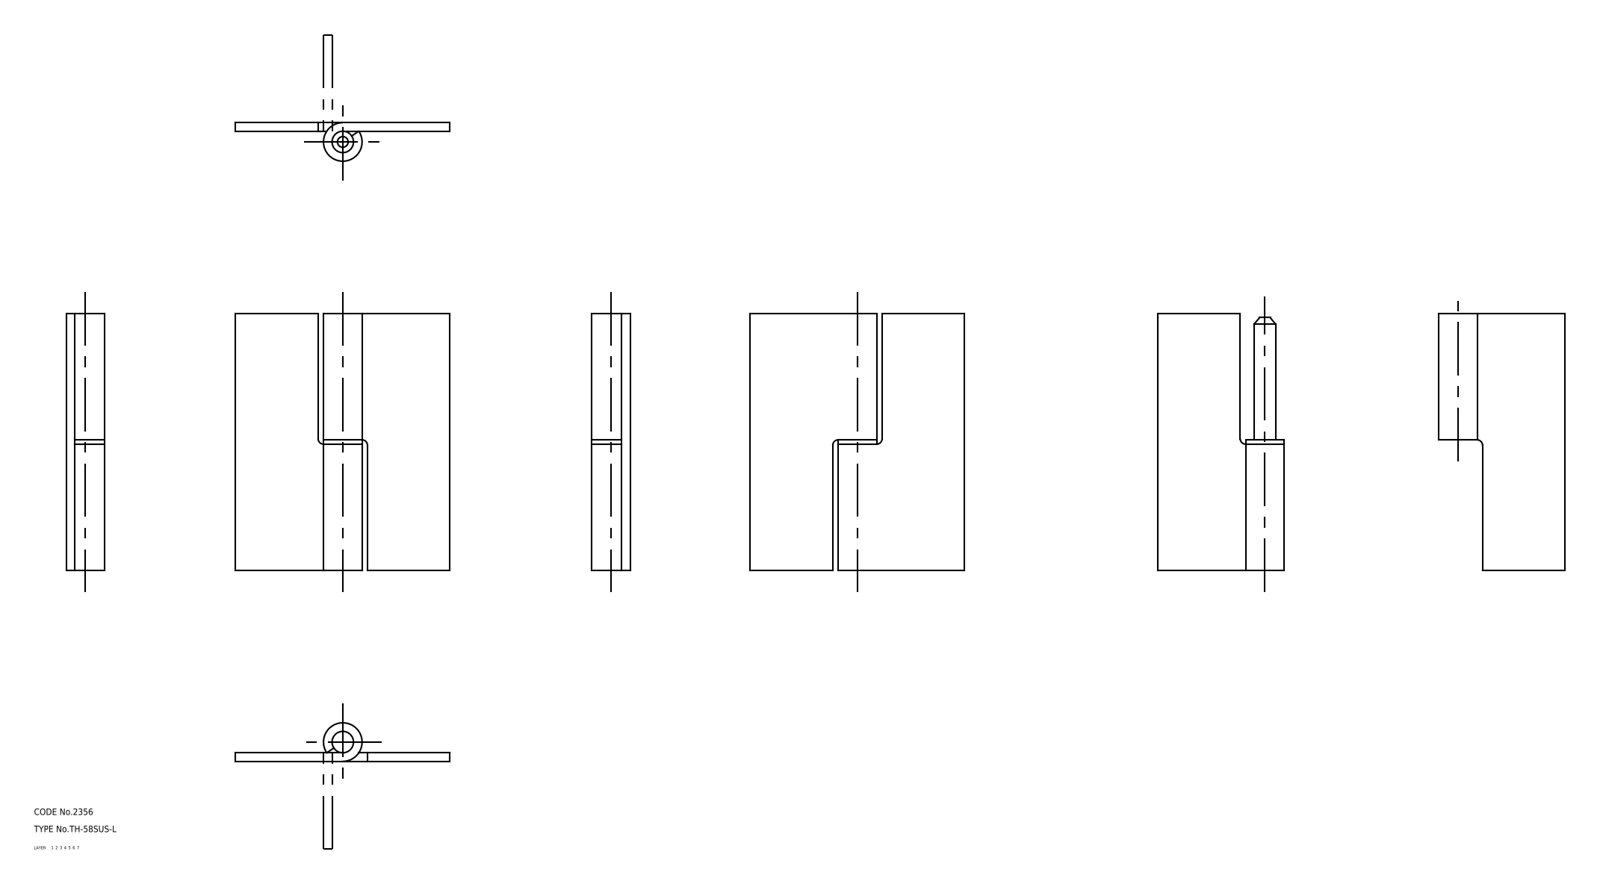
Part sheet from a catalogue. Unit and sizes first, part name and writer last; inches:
Units: inches
Overall size (bounding box): 4.724 × 3.937 × 0.709
Volume: 4.237 in³ · Surface area: 58.24 in²
Bodies: 4 solids, 34 faces (0 planar, 0 cylindrical, 34 other)
Part name (STEP PRODUCT): washer; shaft; hinge piece_B; hinge piece_A (+1 more)
STEP written by: CADfix (AUTOMOTIVE_DESIGN)
